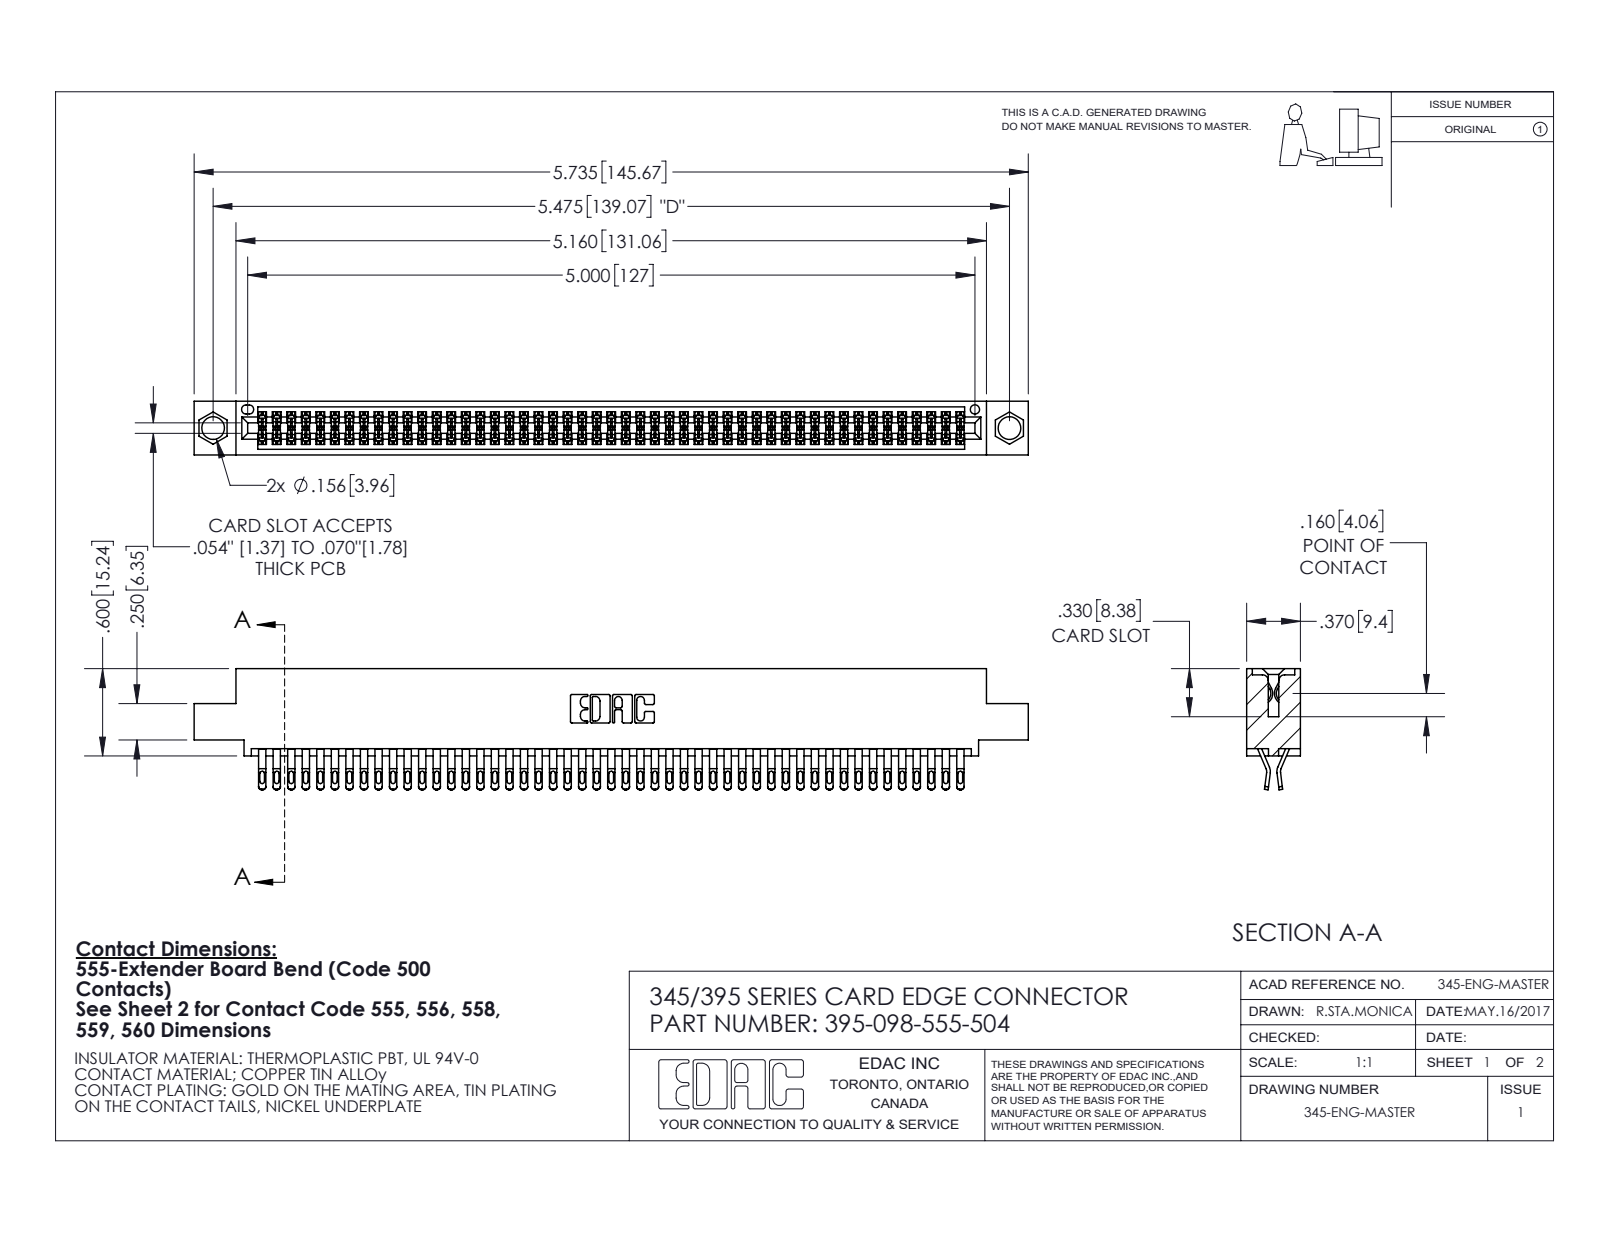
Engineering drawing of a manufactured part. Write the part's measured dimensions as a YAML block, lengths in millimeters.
part_name: "345-292-001_555 Tail; 395-098-555-504; 345 Part_0.110 Offset - 0.156 Dia-TI"
step_written_by: "SolidWorks 2020 (CONFIG_CONTROL_DESIGN)"
units: millimeters
bodies: {solids: 99, faces: 5632, planar: 3136, cylindrical: 2496, other: 0}
overall_size: [145.7, 21.1, 9.4]
volume: 14300
surface_area: 22240
round_holes:
  - {diameter: 4, count: 2}
  - {diameter: 1.6, count: 1}
partial_cylinders:
  - {radius: 0.4, count: 245}
  - {radius: 0.2, count: 196}
  - {radius: 0.5, count: 196}
  - {radius: 0.3, count: 22}
  - {radius: 0.2, count: 6}
  - {radius: 0.8, count: 6}
  - {radius: 0.7, count: 3}
  - {radius: 0.3, count: 2}
face_to_face_distances: [7.6, 1.8, 0.6, 9.4, 5.1, 2.5, 6.9, 5.7, 4.4, 3.8]
hole_center_spacings: [6.9, 133.1, 139.1]
